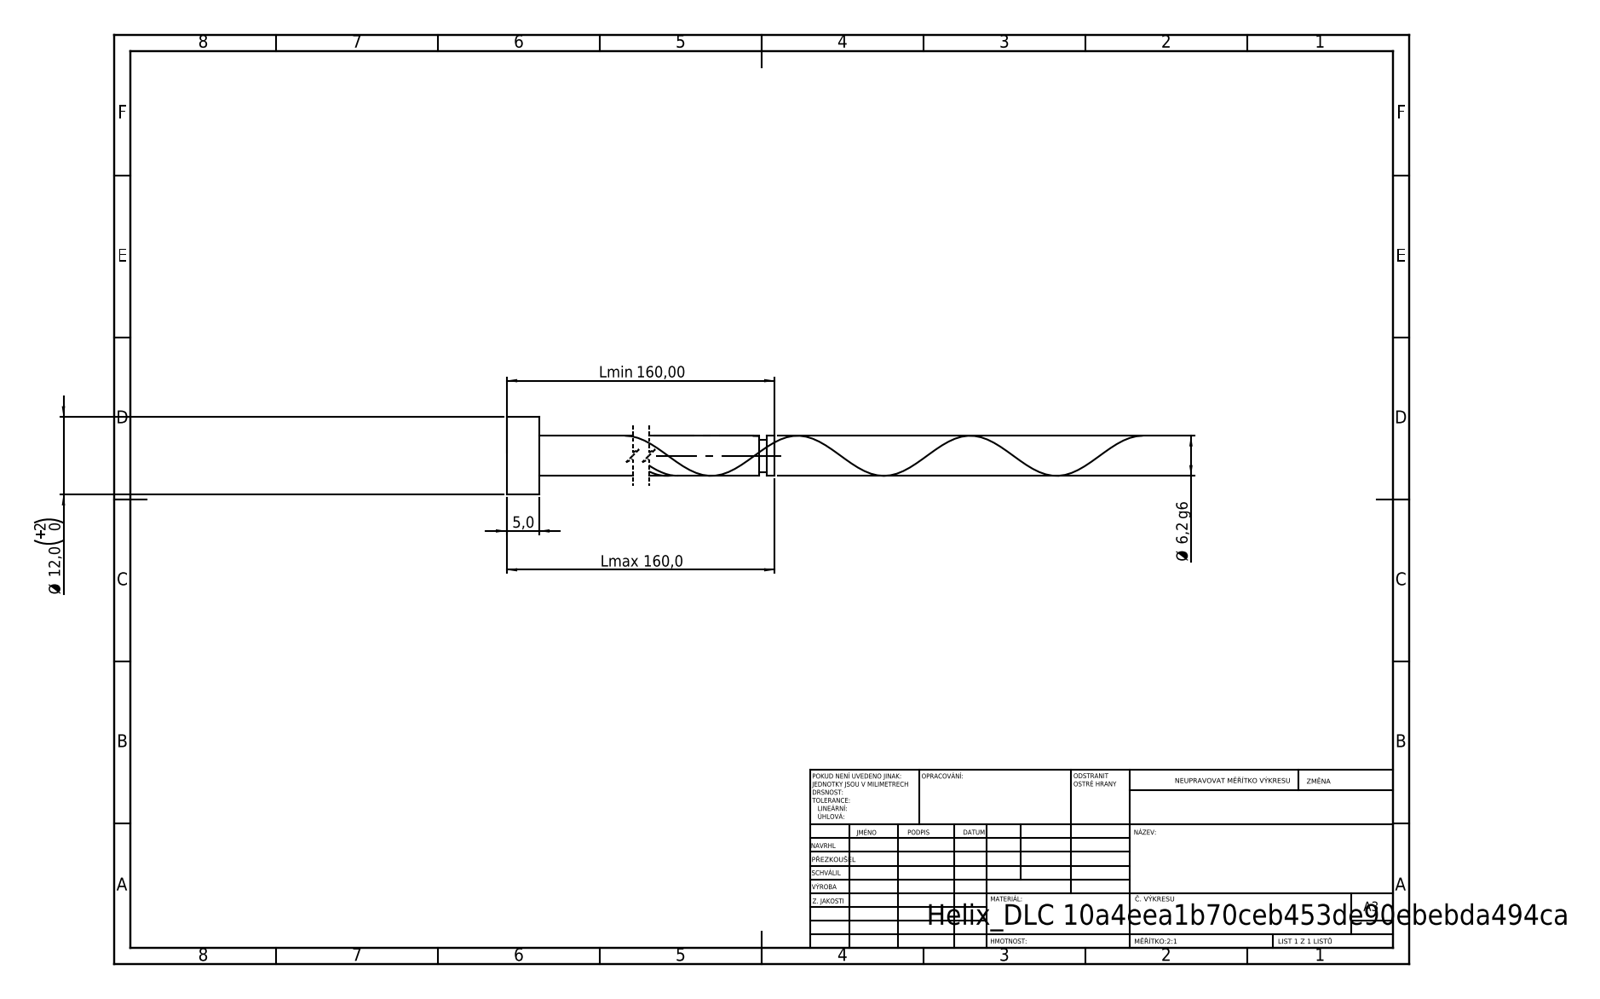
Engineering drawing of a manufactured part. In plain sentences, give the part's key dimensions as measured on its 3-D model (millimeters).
Its 3-D file was written by "SolidWorks 2019 (CONFIG_CONTROL_DESIGN)". It is 1 solid with 21 faces: 6 planar, 14 cylindrical and 1 other. Overall it measures 160 by 12 by 12 millimeters. Its volume is 5 185 cubic millimeters and its surface area 3 514 square millimeters. Round bosses or shafts: 1 of diameter 12, 1 of diameter 6.2, 1 of diameter 4.96. The main face-to-face distances are 5, 160, 155, 158.8, 153.8, 1.2, 157.56, 152.56, 1.24, 2.44.
